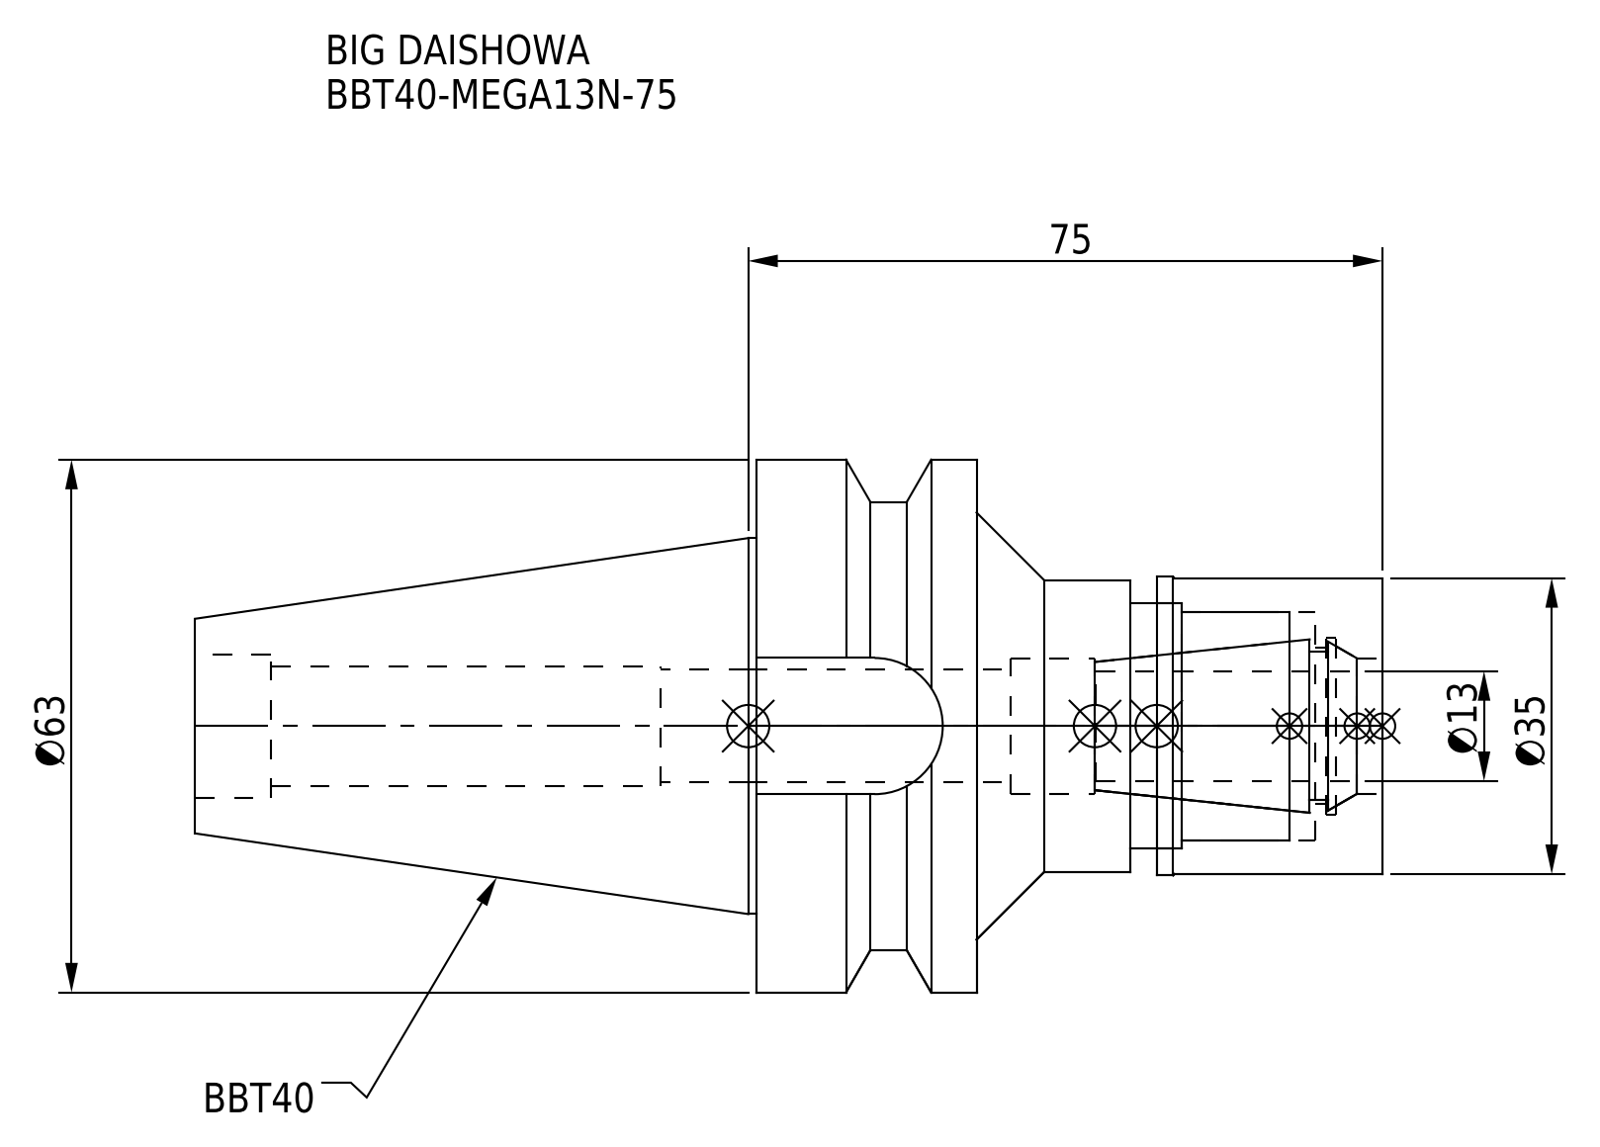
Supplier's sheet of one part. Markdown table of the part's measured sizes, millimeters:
| quantity | value |
| --- | --- |
| part name | MGN13_1.stp; BBT40-MEGA13N-75_1.stp; BBT40-MEGA13N-75; DXF_TEMP_ASSY_ASM_4_ASM.stp (+3 more) |
| STEP written by | SolidWorks 2019 (CONFIG_CONTROL_DESIGN) |
| units | millimeters |
| bodies | 2 solids, 76 faces (22 planar, 40 cylindrical, 14 other) |
| overall size | 140.4 × 63 × 63 |
| volume | 157 970 mm³ |
| surface area | 34 292 mm² |
| round holes (diameter × count) | 13.3 × 1, 13.31 × 1, 14.2 × 1, 16 × 1, 17 × 1, 18.5 × 1, 21 × 1, 27 × 1, 29 × 1 |
| round bosses / shafts (diameter × count) | 63 × 1, 53 × 1, 44.45 × 1, 35.3 × 1, 35 × 1, 34.5 × 1 |
| partial cylindrical surfaces (radius × count) | 8.05 × 1 |
| main face-to-face distances | 26, 48, 74, 45, 40, 26.7, 21.3, 47.3, 8, 18.7 |
